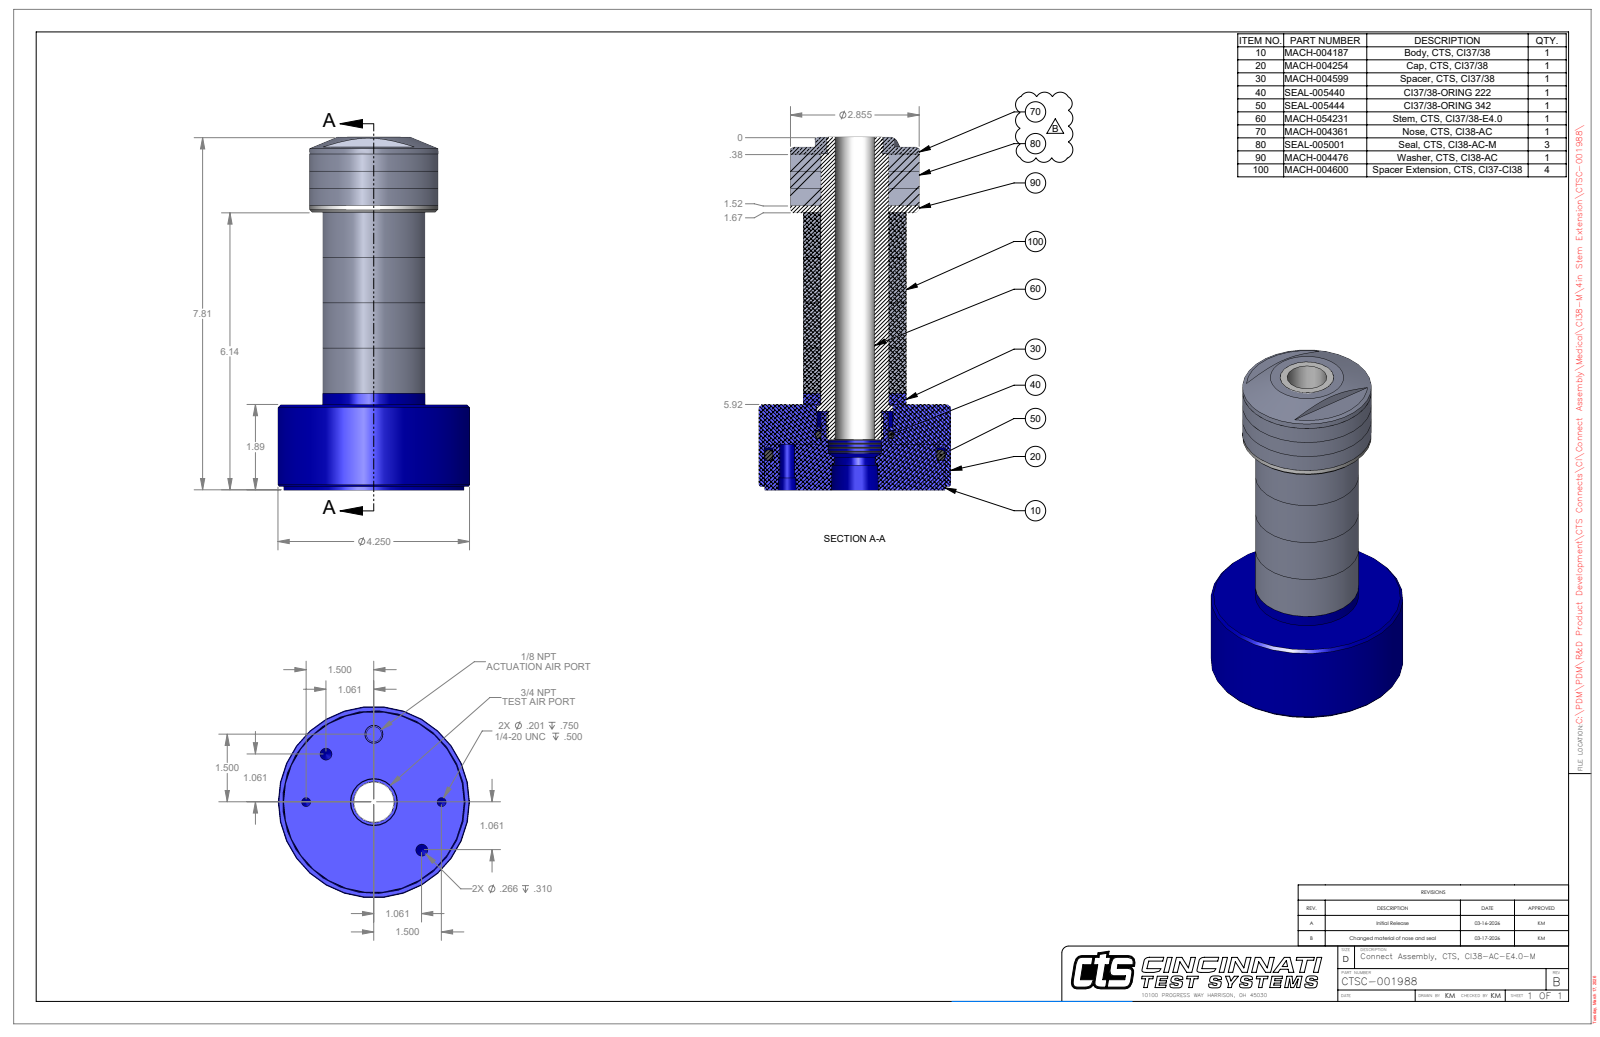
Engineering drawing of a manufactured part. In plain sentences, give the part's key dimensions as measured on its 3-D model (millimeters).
The part is named "CTSC-001988". Its 3-D file was written by "SolidWorks 2023 (AUTOMOTIVE_DESIGN)". It is 11 solids with 89 faces: 43 planar, 34 cylindrical and 12 other. Overall it measures 198.45 by 107.95 by 107.95 millimeters. Its volume is 798 793 cubic millimeters and its surface area 161 158 square millimeters. Round holes: 2 of diameter 5.11, 2 of diameter 6.75, 1 of diameter 22.35, 1 of diameter 23.01, 1 of diameter 29.77, 1 of diameter 37.97, 1 of diameter 37.97, 1 of diameter 38.35, 1 of diameter 42.88, 1 of diameter 101.6. Round bosses or shafts: 1 of diameter 107.95, 1 of diameter 101.4, 1 of diameter 72.52, 1 of diameter 72.52, 1 of diameter 57.94, 1 of diameter 42.52, 1 of diameter 38.05, 1 of diameter 31.75. The main face-to-face distances are 9.65, 19.31, 25.4, 50.8, 48.08, 188.85, 140.77, 179.2, 131.12, 169.54. The hole center spacings are 38.1, 29.16, 70.4, 76.2.
